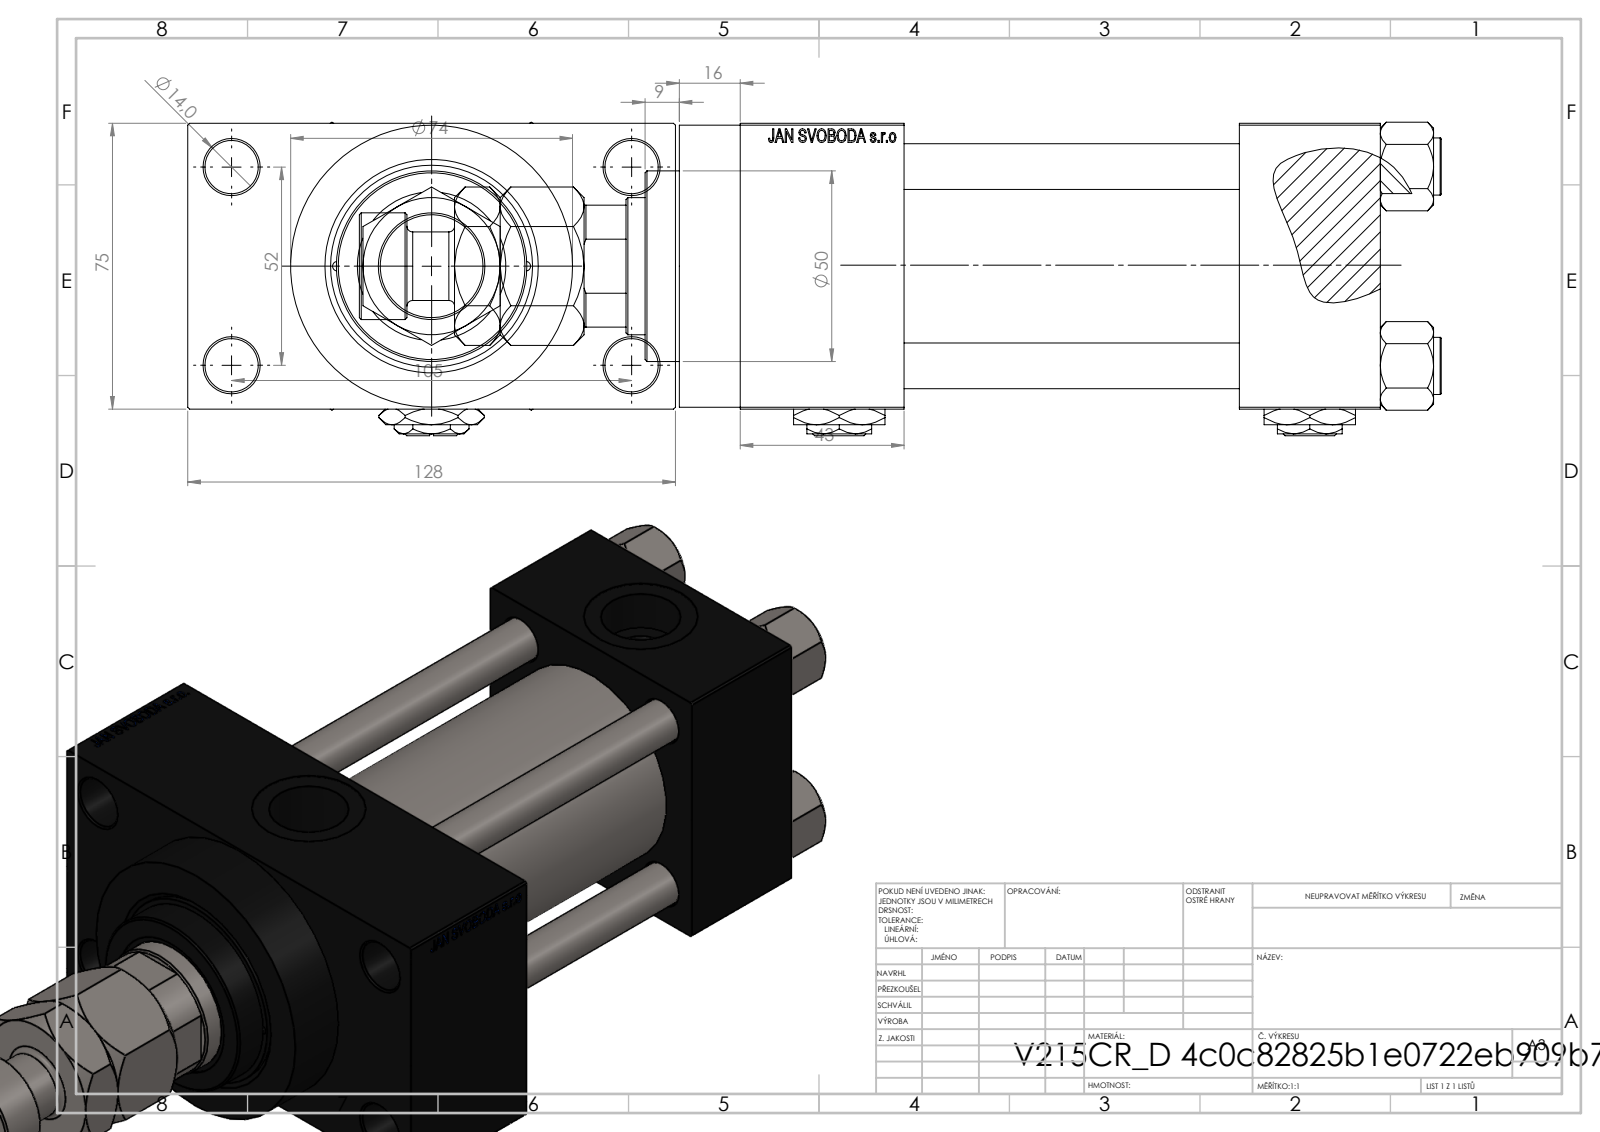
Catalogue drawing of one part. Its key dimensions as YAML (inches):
part_name: "V215_VC_A; Zatka_pro_OIL_PORT; V215CR_VCP_D; MFA (+3 more)"
step_written_by: "SolidWorks 2019 (CONFIG_CONTROL_DESIGN)"
units: inches
bodies: {solids: 14, faces: 1267, planar: 565, cylindrical: 108, other: 594}
overall_size: [11.181, 5.039, 3.239]
volume: 56.72
surface_area: 317.3
round_holes:
  - {diameter: 0.472, count: 4}
  - {diameter: 0.551, count: 4}
  - {diameter: 0.098, count: 2}
  - {diameter: 0.276, count: 2}
  - {diameter: 0.825, count: 2}
  - {diameter: 1.181, count: 2}
  - {diameter: 1.004, count: 1}
  - {diameter: 1.417, count: 1}
  - {diameter: 1.535, count: 1}
  - {diameter: 1.614, count: 1}
  - {diameter: 2.087, count: 1}
round_bosses_or_shafts:
  - {diameter: 0.591, count: 4}
  - {diameter: 2.913, count: 1}
  - {diameter: 2.205, count: 1}
  - {diameter: 1.969, count: 1}
  - {diameter: 1.102, count: 1}
  - {diameter: 0.709, count: 1}
partial_cylinders:
  - {radius: 0.689, count: 1}
face_to_face_distances: [2.953, 3.465, 1.457, 4.921, 3.996, 1.043, 6.614, 1.693, 5.157, 2.323]
hole_center_spacings: [1.031, 1.037, 1.456, 1.497, 2.059, 2.253, 2.3, 2.307]
